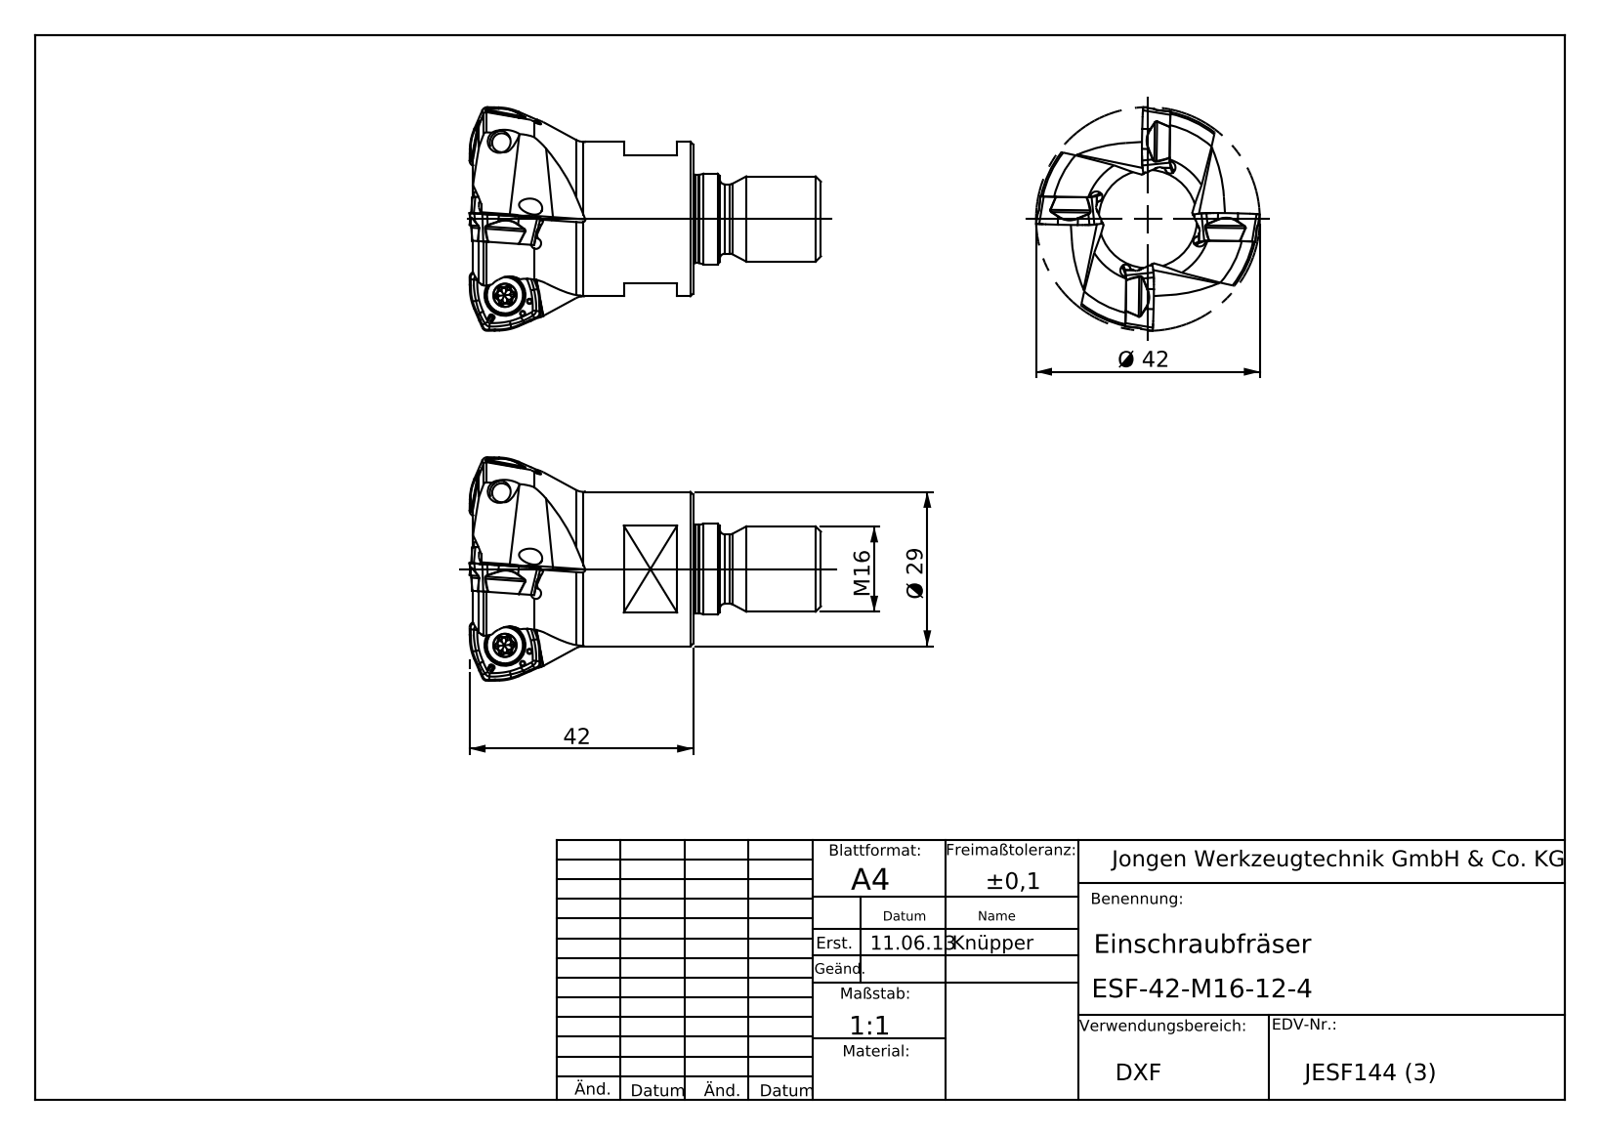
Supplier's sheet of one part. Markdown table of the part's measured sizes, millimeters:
| quantity | value |
| --- | --- |
| part name | ESF-42-M16-12-4 |
| STEP written by | SolidWorks 2013 (AUTOMOTIVE_DESIGN) |
| units | millimeters |
| bodies | 1 solid, 213 faces (87 planar, 51 cylindrical, 75 other) |
| overall size | 65.94 × 41.97 × 41.97 |
| volume | 37 620 mm³ |
| surface area | 9 622 mm² |
| round holes (diameter × count) | 3 × 4, 4 × 1 |
| round bosses / shafts (diameter × count) | 29 × 1, 17 × 1, 16.56 × 1, 16 × 1, 13 × 1 |
| partial cylindrical surfaces (radius × count) | 0.5 × 8, 1.3 × 8, 1 × 4, 2 × 4 |
| main face-to-face distances | 24, 39.75, 63.75, 37, 13, 26.75, 27, 3, 10, 36.75 |
